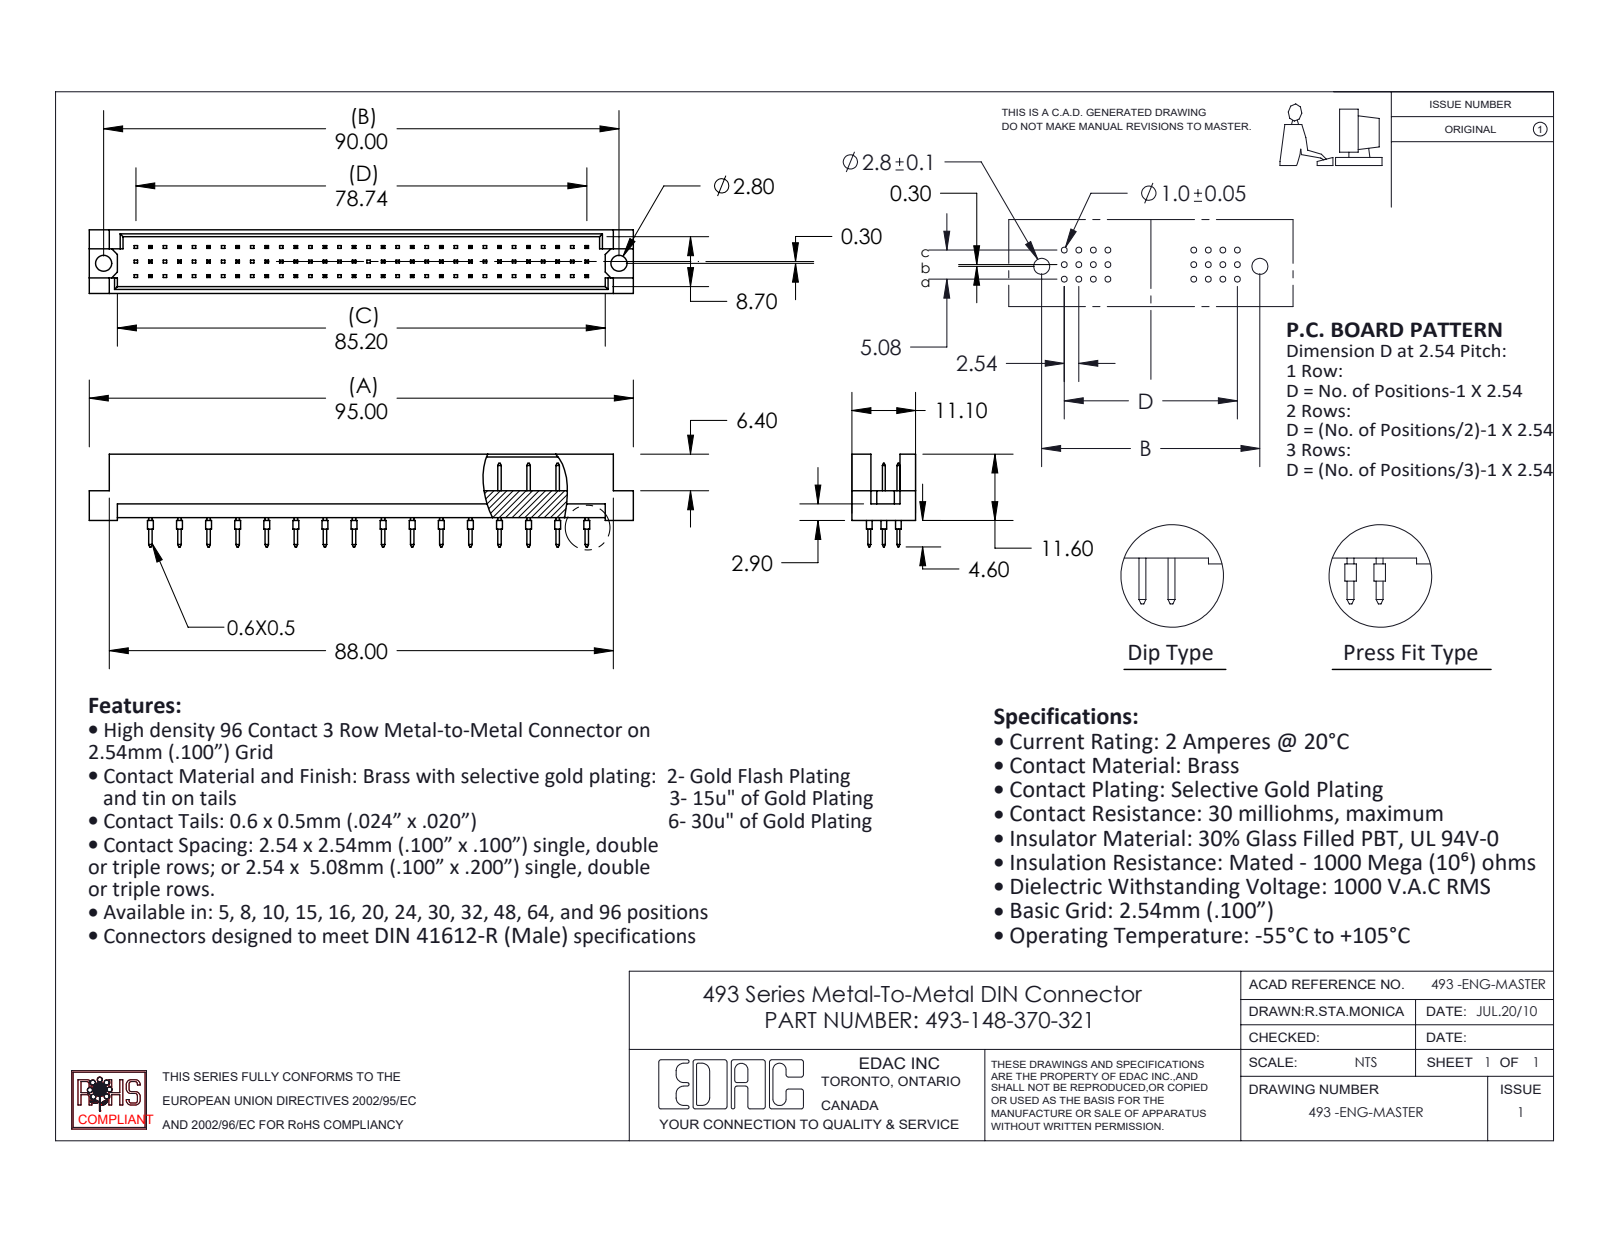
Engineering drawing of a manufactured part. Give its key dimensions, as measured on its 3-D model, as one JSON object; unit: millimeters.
{"part_name": "493-148-370-321; 493-290_70; 493 Part_96", "step_written_by": "SolidWorks 2020 (CONFIG_CONTROL_DESIGN)", "units": "millimeters", "bodies": {"solids": 49, "faces": 1492, "planar": 1392, "cylindrical": 100, "other": 0}, "overall_size": [95, 16.2, 11.1], "volume_mm3": 5899, "surface_area_mm2": 8112, "round_holes": [[2.8, 2]], "round_bosses_or_shafts": [[1, 48]], "face_to_face_distances": [1.2, 9.9, 11.1, 2.54, 8.7, 5.08, 0.5, 4.7, 4.6, 2.76], "hole_center_spacings": [90]}
